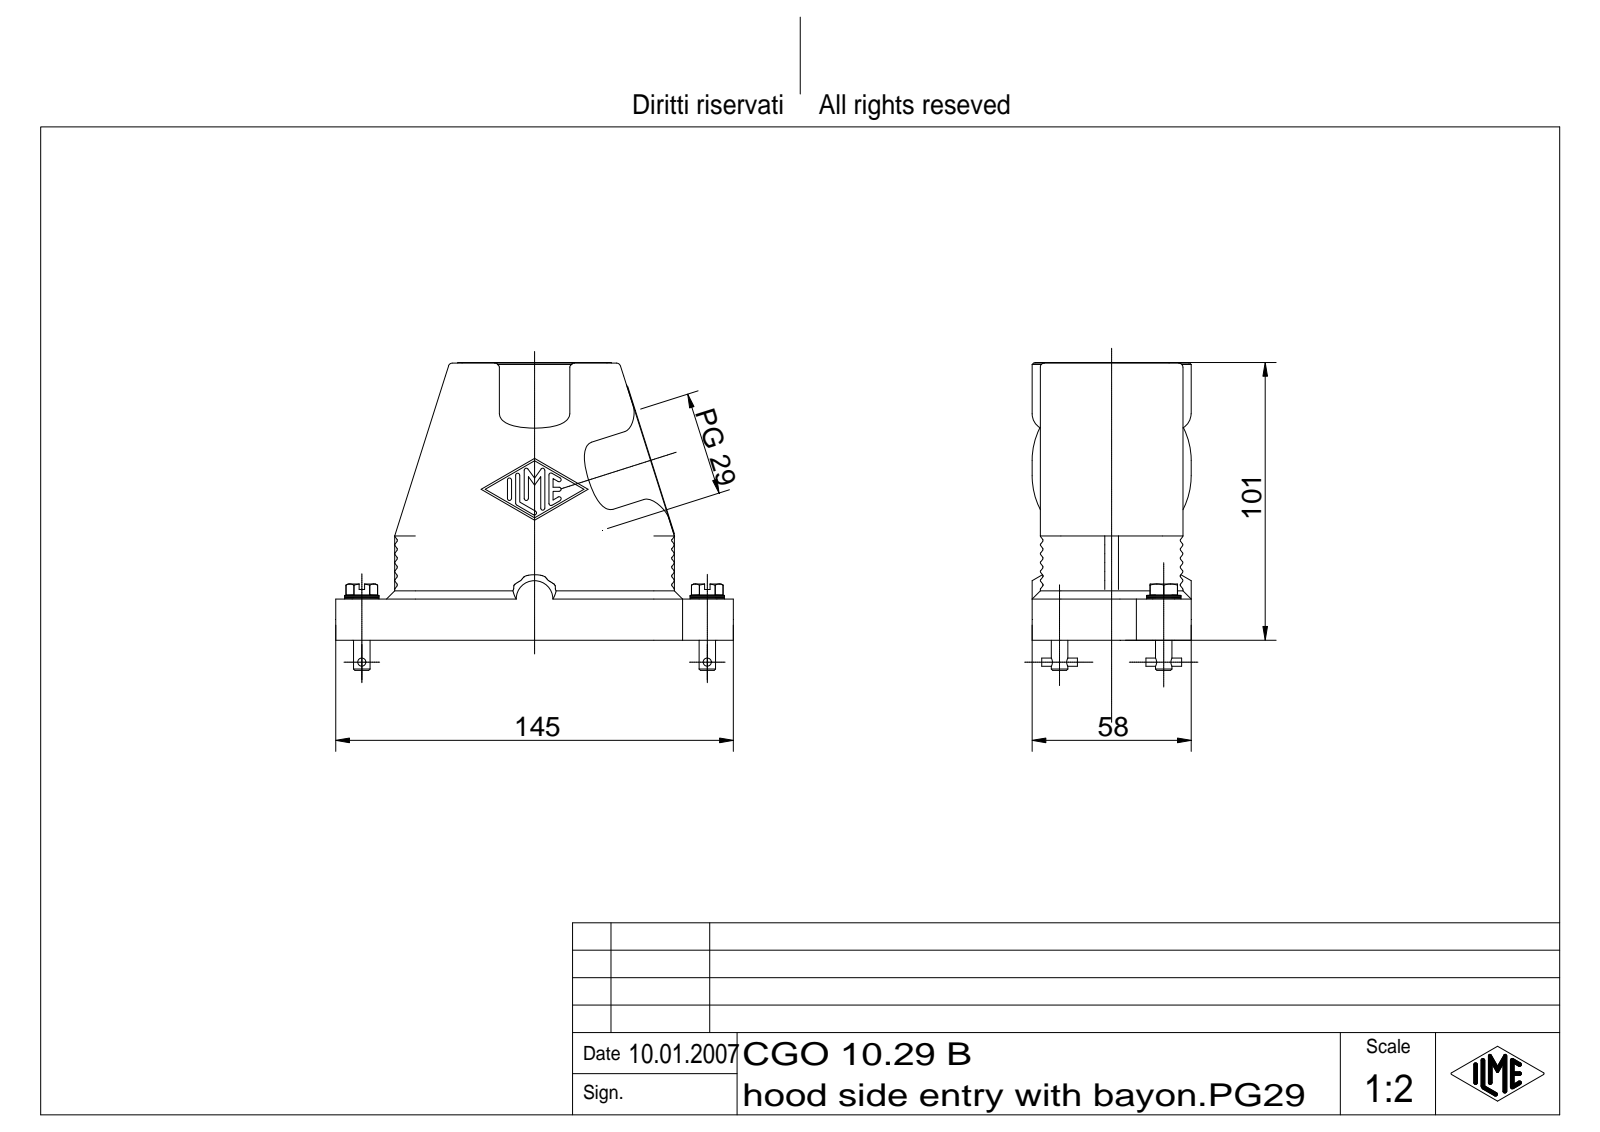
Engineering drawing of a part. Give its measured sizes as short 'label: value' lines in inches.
name: CGO 10.29 B
written by: Autodesk Inventor 7 (AUTOMOTIVE_DESIGN)
unit: in
bodies: 3 solids, 793 faces (198 planar, 211 cylindrical, 384 other)
size: 5.709 × 4.417 × 2.283
volume: 12 in³; area: 112.8 in²
holes: 2× ⌀0.097, 2× ⌀0.126, 2× ⌀0.26, 2× ⌀0.591, 1× ⌀1.397
bosses: 2× ⌀2.205, 2× ⌀0.492, 2× ⌀0.236, 2× ⌀0.118, 1× ⌀2.283
rounds: 39× R0.02, 14× R0.03, 8× R0.295, 6× R0.236, 4× R0.059, 4× R0.118, 2× R0.226, 2× R0.413
face distances: 0.118, 2.047, 1.929, 0.236, 2.165, 0.098, 1.811, 0.02, 2.283, 0.138
hole spacings: 1.376, 3.823, 2.483, 5.181
